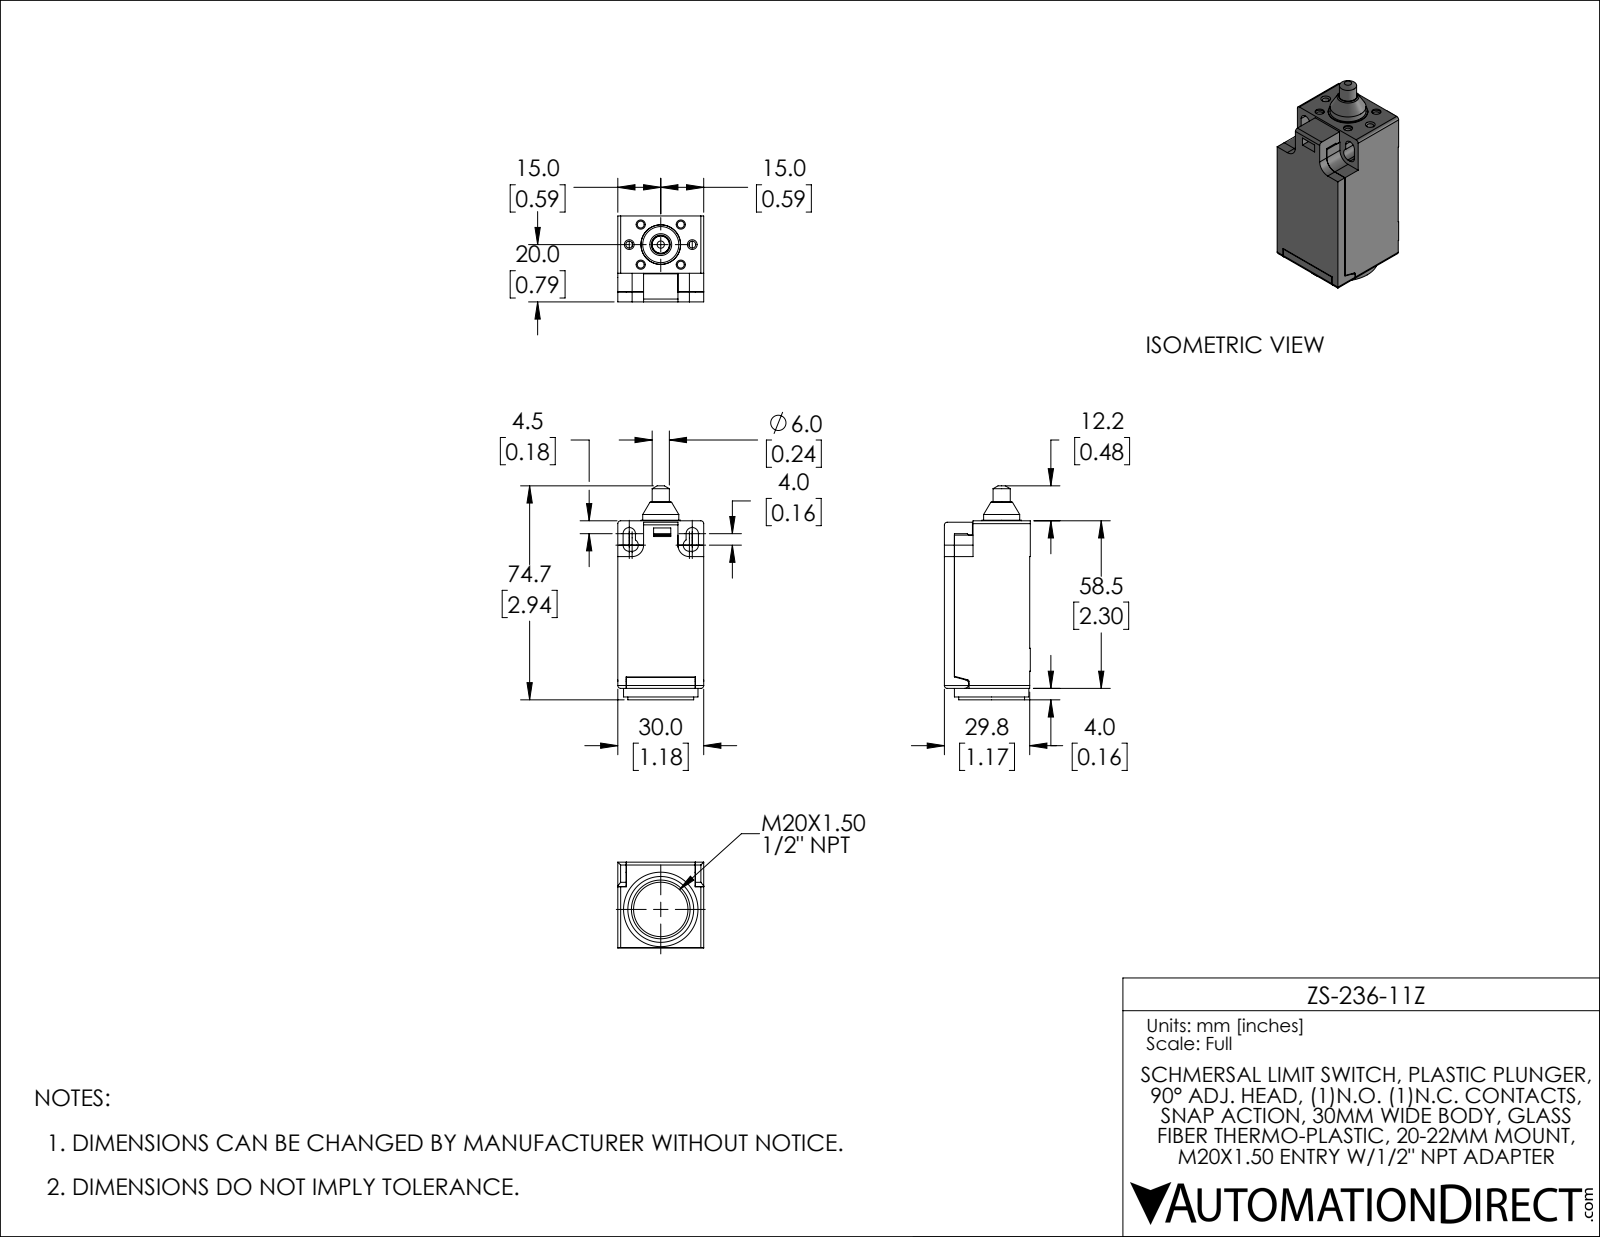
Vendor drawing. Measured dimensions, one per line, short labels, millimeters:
name: ZS-236-11Z
written by: SolidWorks 2019 (AUTOMOTIVE_DESIGN)
unit: mm
bodies: 2 solids, 131 faces (79 planar, 42 cylindrical, 10 other)
size: 74.7 × 30 × 30
volume: 48 190 mm³; area: 14 630 mm²
holes: 6× ⌀2.4, 4× ⌀3.2, 1× ⌀6.2, 1× ⌀13.8, 1× ⌀19
bosses: 1× ⌀26, 1× ⌀23, 1× ⌀13.8, 1× ⌀12.6, 1× ⌀6
rounds: 6× R1, 6× R2.2, 2× R4, 1× R0.6, 1× R1.5
face distances: 30, 3.5, 26.3, 29.8, 26.5, 6, 10, 52.5, 4, 9
hole spacings: 8.1, 9.9, 14, 19.3, 7.8, 11, 11.5, 12.6
